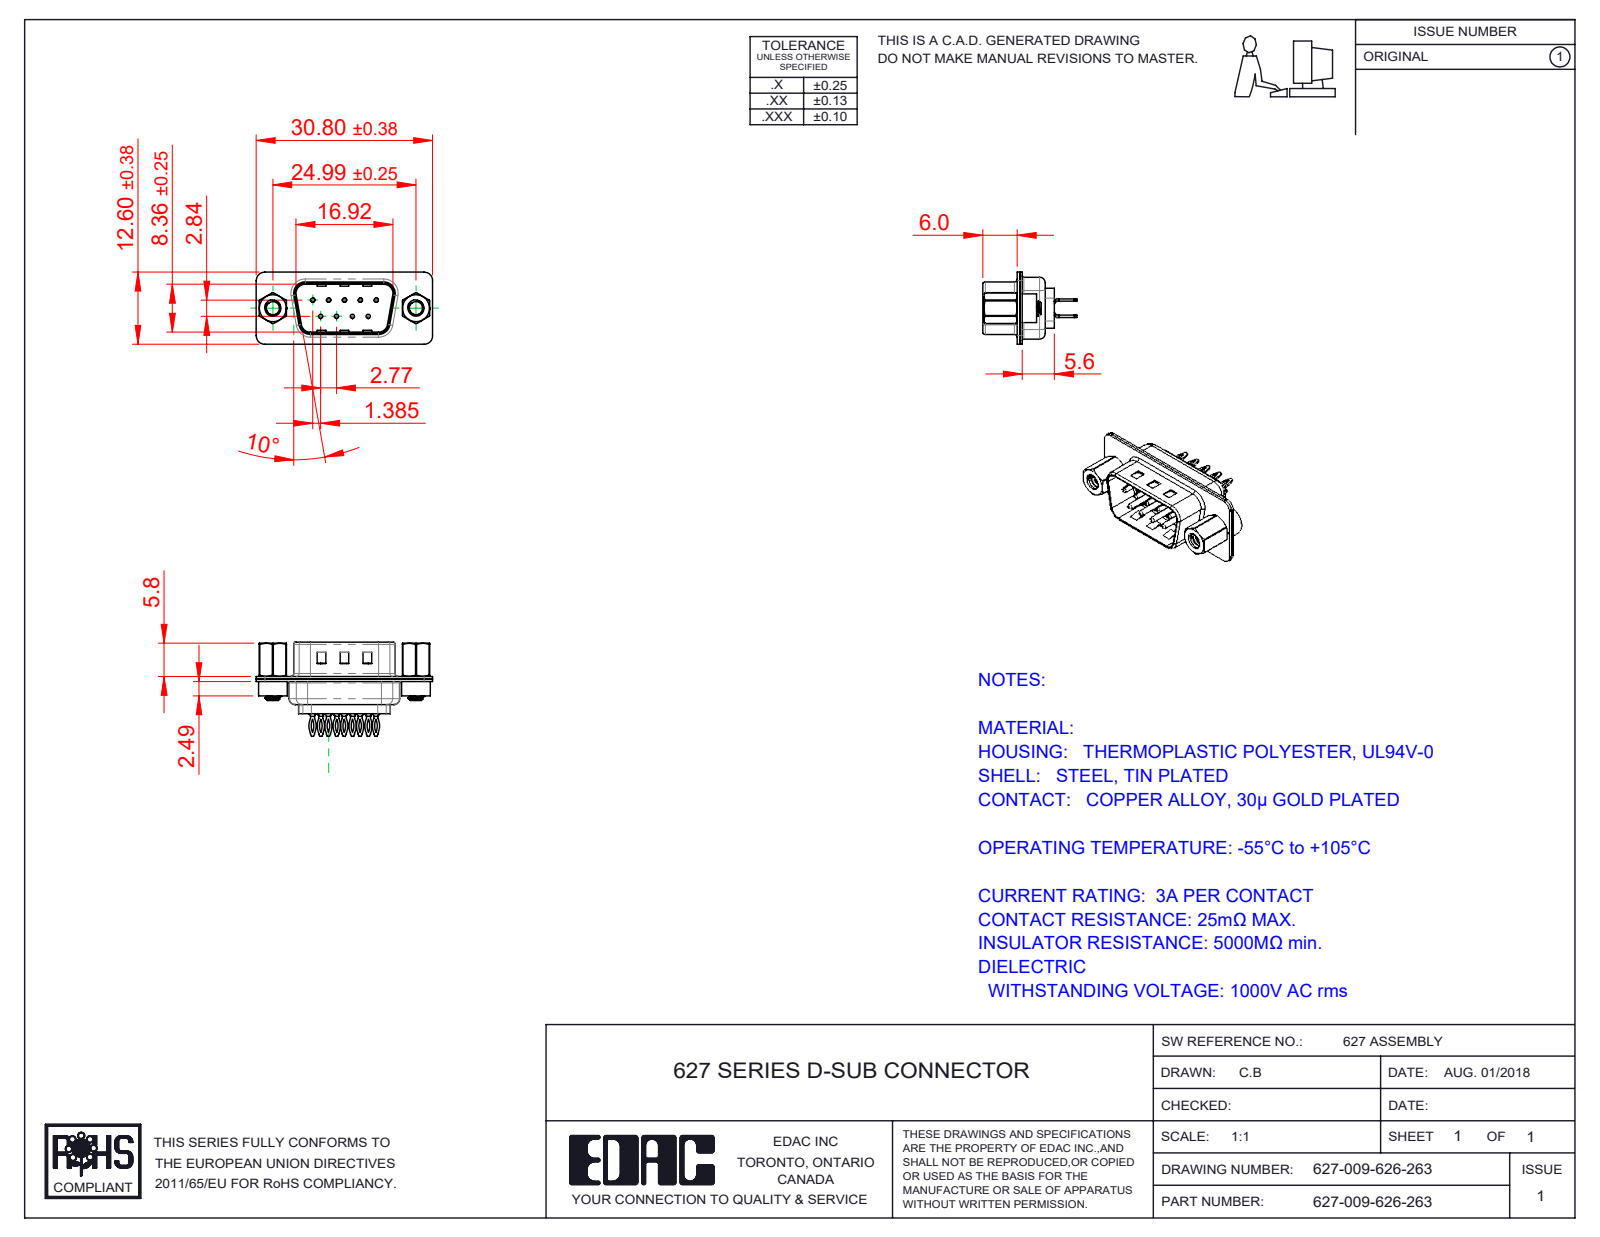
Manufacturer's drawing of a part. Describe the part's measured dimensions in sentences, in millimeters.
The part is named "627 Shell Rear_09 Contacts; 627 Contact Row 2_26L; 627 Shell Front_09 Contacts; 627 Contact Row 1_26L (+4 more)". Its 3-D file was written by "SolidWorks 2020 (CONFIG_CONTROL_DESIGN)". It is 16 solids with 1110 faces: 309 planar, 478 cylindrical and 323 other. Overall it measures 30.8 by 16.45 by 12.6 millimeters. Its volume is 1 519 cubic millimeters and its surface area 4 378 square millimeters. Round holes: 9 of diameter 0.35, 9 of diameter 1.1, 9 of diameter 1.6, 2 of diameter 2.26, 2 of diameter 2.29, 2 of diameter 4, 2 of diameter 4.8. Round bosses or shafts: 9 of diameter 2, 9 of diameter 1.5, 9 of diameter 0.75, 2 of diameter 5, 2 of diameter 4.9, 2 of diameter 2.79. Partial cylindrical surfaces (rounded edges, fillets, slot ends): 18 of radius 1.5, 18 of radius 2.92, 18 of radius 3.33, 12 of radius 2, 8 of radius 0.5, 8 of radius 1.6, 4 of radius 0.25, 4 of radius 0.6. The main face-to-face distances are 0.45, 0.4, 0.9, 0.82, 9.58, 1.4, 8.76, 0.5, 1.5, 6.05. The hole center spacings are 3.16, 2.77, 5.54, 5.03, 5.04, 8.31, 7.48, 7.49.
